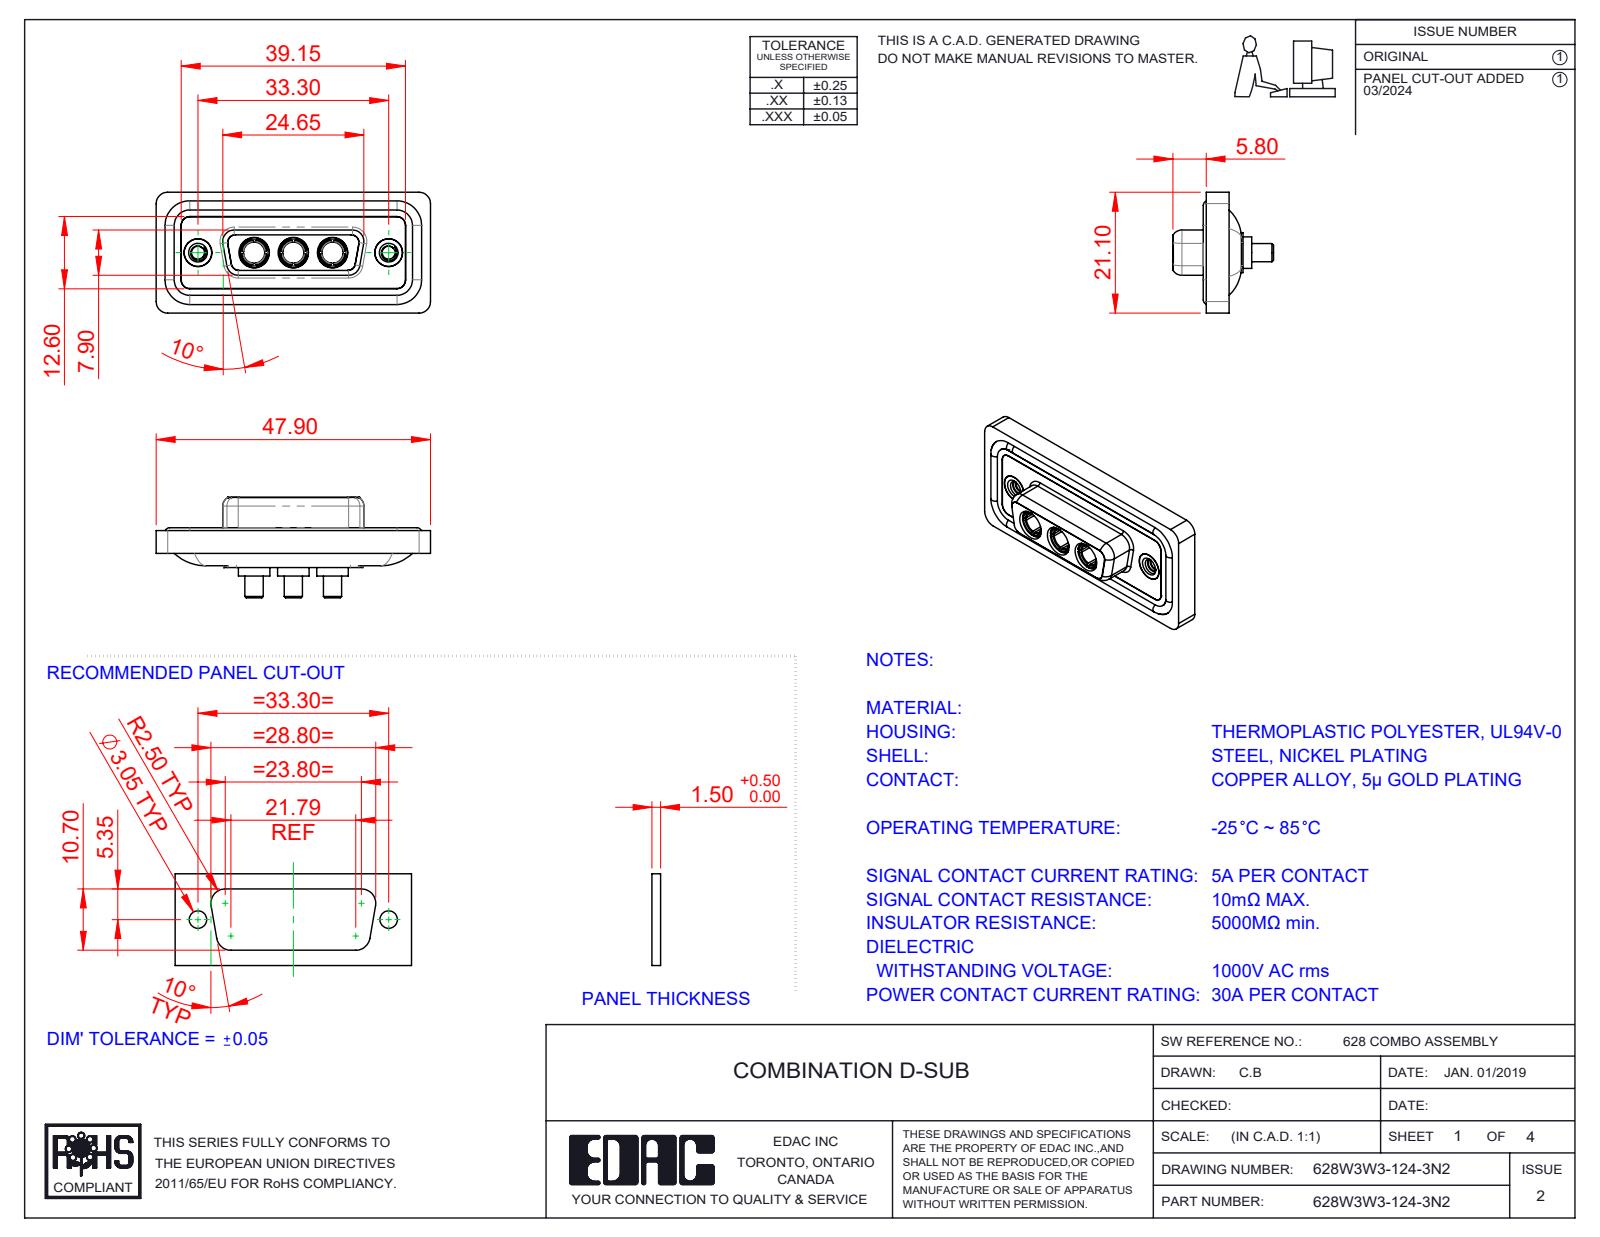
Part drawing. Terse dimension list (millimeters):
name: 628Combo Waterproof Housing_15 Contacts; 628Combo Shell Rear_15 Contacts; 628Combo Threaded Rivet_2; 628Combo Shell Front_15 Contacts (+3 more)
written by: SolidWorks 2023 (CONFIG_CONTROL_DESIGN)
unit: mm
bodies: 13 solids, 608 faces (192 planar, 257 cylindrical, 159 other)
size: 47.9 × 21.1 × 17.55
volume: 6 048 mm³; area: 9 752 mm²
holes: 5× ⌀4.85, 3× ⌀3.7, 3× ⌀5.3, 2× ⌀2.26, 2× ⌀4, 2× ⌀4.05, 2× ⌀5
bosses: 4× ⌀1.6, 3× ⌀5.5, 3× ⌀5.2, 3× ⌀4.96, 3× ⌀4.75, 3× ⌀3.75, 3× ⌀3.2, 2× ⌀4.95
rounds: 22× R1.5, 20× R2, 12× R1.35, 8× R1.6, 4× R0.25, 4× R0.5, 4× R0.6, 4× R0.65
face distances: 0.4, 1.8, 1.6, 0.5, 7.45, 1.1, 2.9, 5.65, 7.05, 6.6
hole spacings: 6.85, 9.8, 16.65, 23.5, 13.7, 33.3
